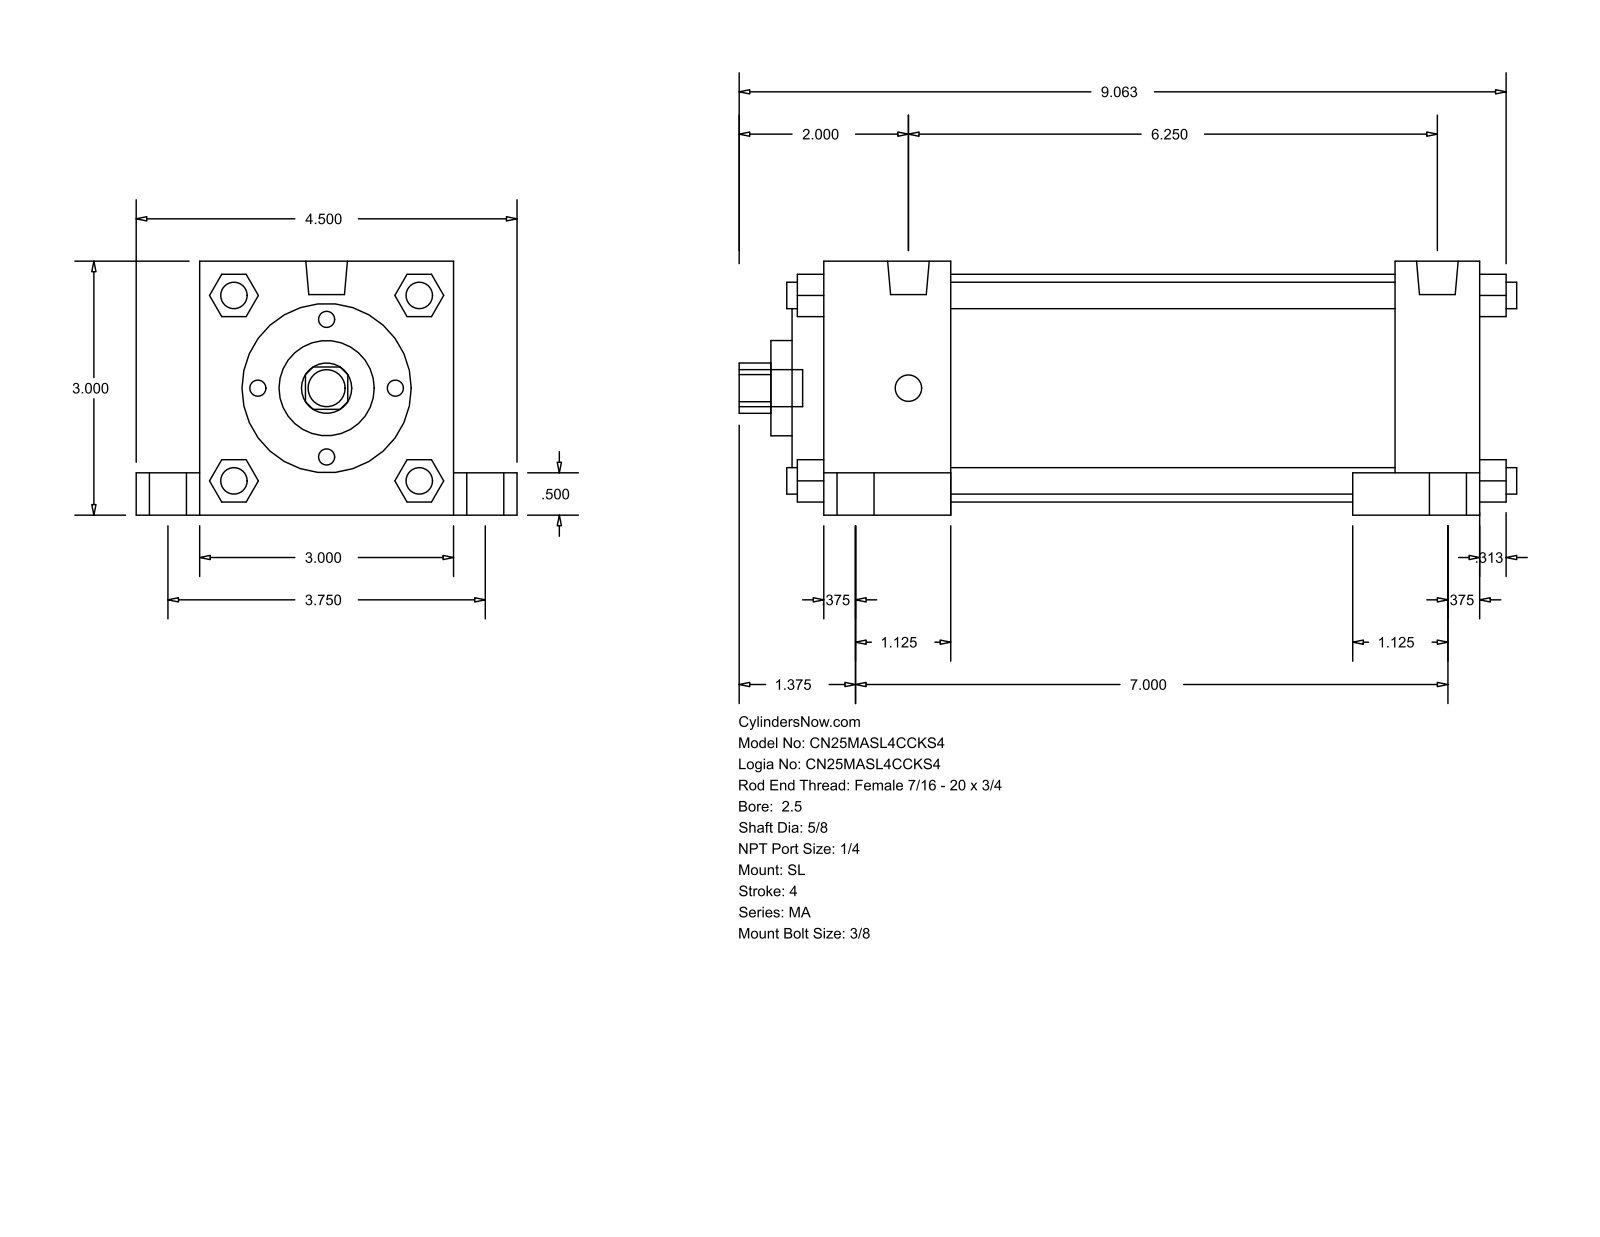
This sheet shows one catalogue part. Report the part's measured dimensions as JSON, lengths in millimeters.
{"part_name": "MA_SL__0250_0.625", "step_written_by": "GSSL Pune (CONFIG_CONTROL_DESIGN)", "units": "millimeters", "bodies": {"solids": 0, "faces": 150, "planar": 113, "cylindrical": 37, "other": 0}, "overall_size": [233.36, 114.3, 76.2], "round_holes": [[15.88, 1], [28.57, 1], [50.8, 1], [68.33, 1]], "round_bosses_or_shafts": [[7.94, 8], [11.11, 5], [17.46, 4], [12.49, 2]], "partial_cylinders_radius": [[7.54, 1]], "face_to_face_distances": [76.2, 196.85, 12.7, 133.35, 25.4, 38.1, 158.75, 171.45, 19.05, 63.5]}
